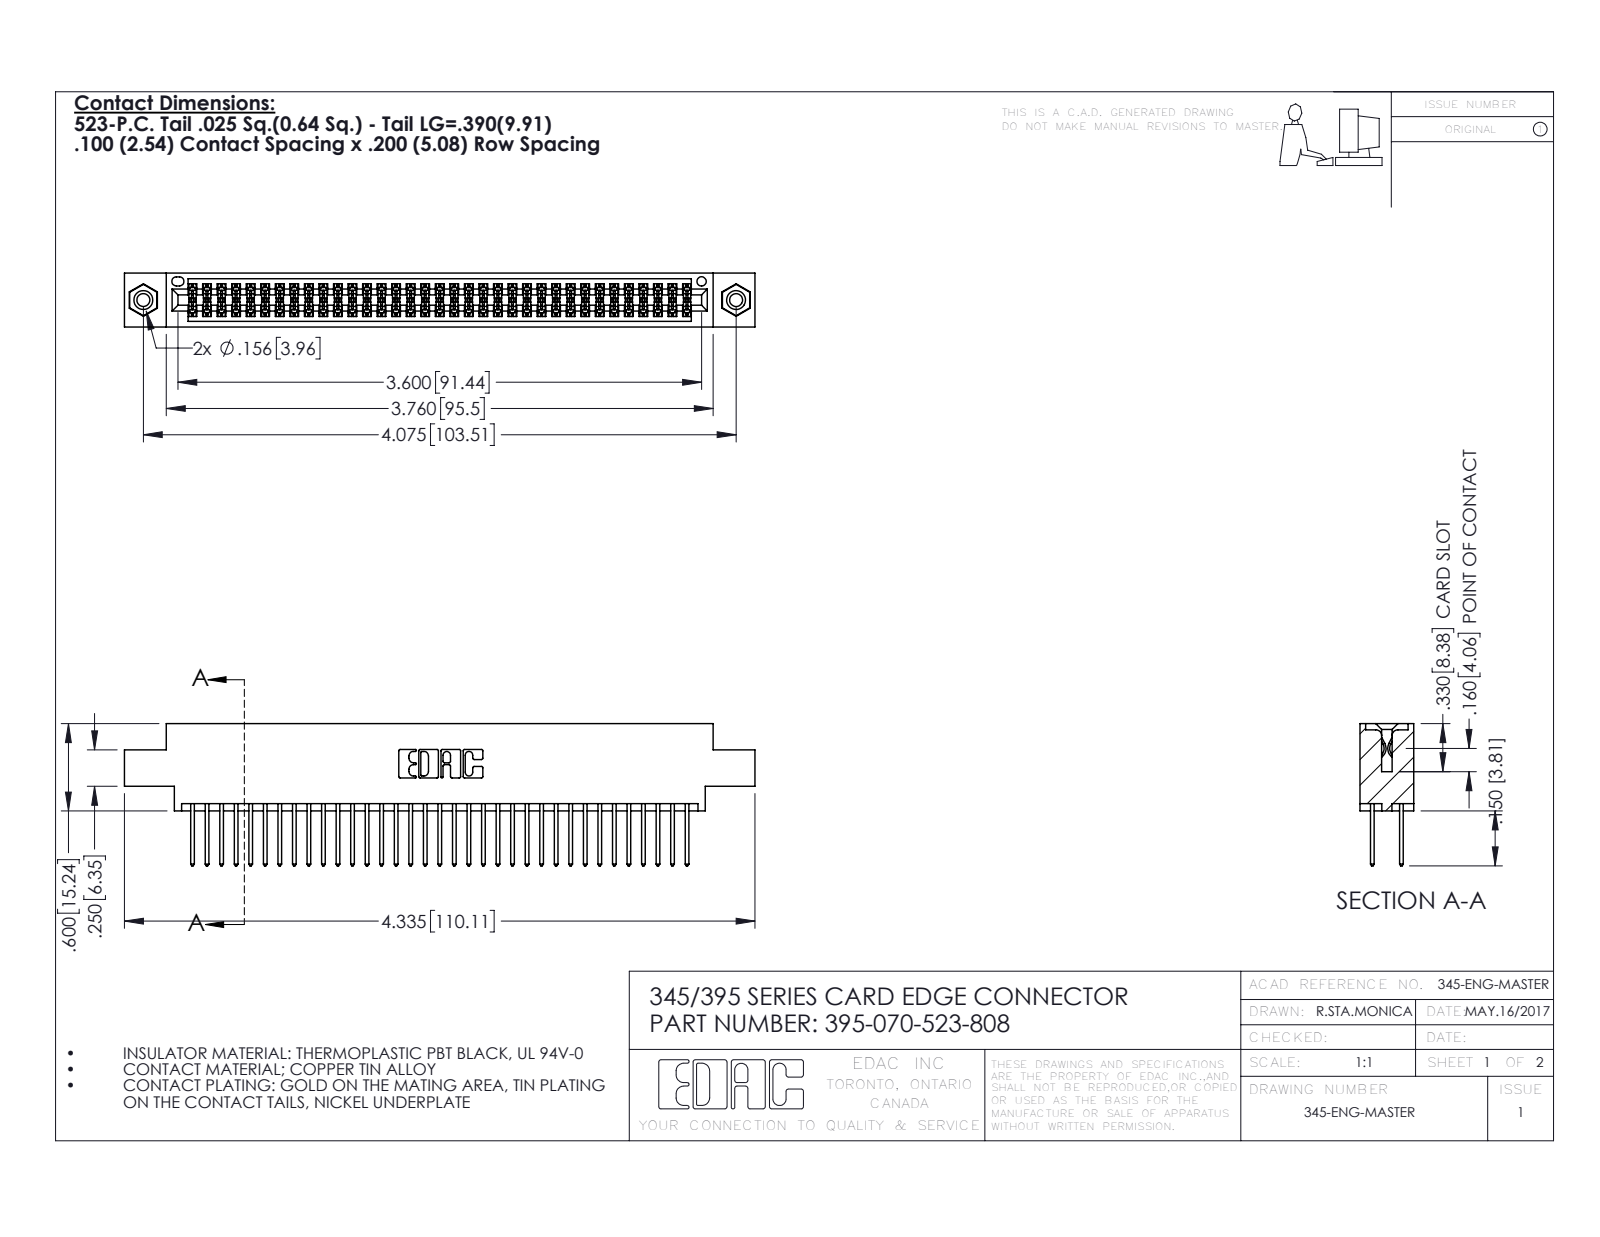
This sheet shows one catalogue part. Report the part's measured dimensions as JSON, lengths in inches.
{"part_name": "345 Part_0.170 Offset - 0.156 Dia-TI; 395-070-523-808; 345-292-001_345-293-123; 345-250-001_345-250-003-102", "step_written_by": "SolidWorks 2016 (CONFIG_CONTROL_DESIGN)", "units": "inches", "bodies": {"solids": 73, "faces": 3690, "planar": 2426, "cylindrical": 1248, "other": 16}, "overall_size": [4.335, 0.977, 0.37], "volume_in3": 0.65, "surface_area_in2": 25.44, "round_holes": [[0.089, 2], [0.125, 2], [0.156, 2], [0.064, 1]], "round_bosses_or_shafts": [[0.155, 2]], "partial_cylinders_radius": [[0.006, 105], [0.01, 70], [0.01, 22], [0.007, 6], [0.031, 6], [0.026, 3], [0.014, 2], [0.019, 2]], "face_to_face_distances": [0.072, 0.298, 0.2, 0.098, 0.272, 0.025, 0.37, 0.225, 0.175, 0.149], "hole_center_spacings": [0.27, 3.839, 4.075]}
